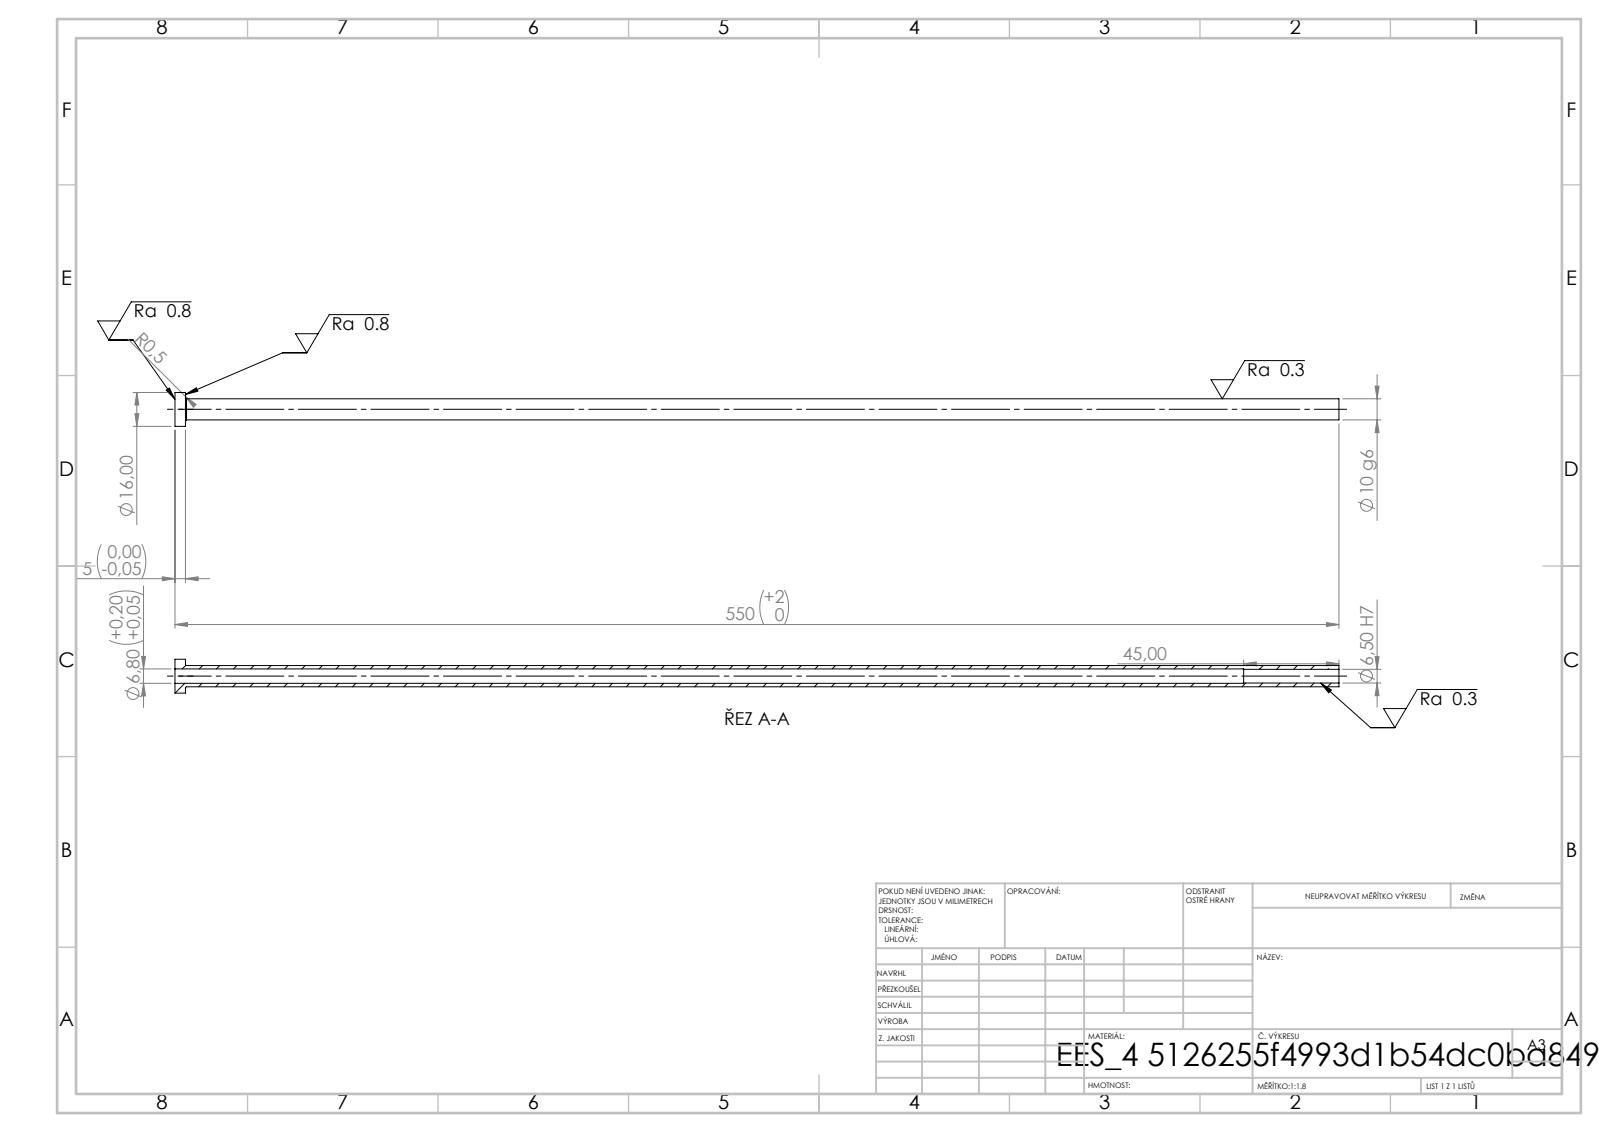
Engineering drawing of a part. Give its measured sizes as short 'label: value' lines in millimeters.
written by: SolidWorks 2019 (CONFIG_CONTROL_DESIGN)
unit: mm
bodies: 1 solid, 14 faces (4 planar, 8 cylindrical, 2 other)
size: 550 × 16 × 16
volume: 23 978 mm³; area: 29 409 mm²
holes: 1× ⌀6.5, 1× ⌀6.8
bosses: 1× ⌀16, 1× ⌀10
face distances: 5, 550, 545, 505, 500, 45
